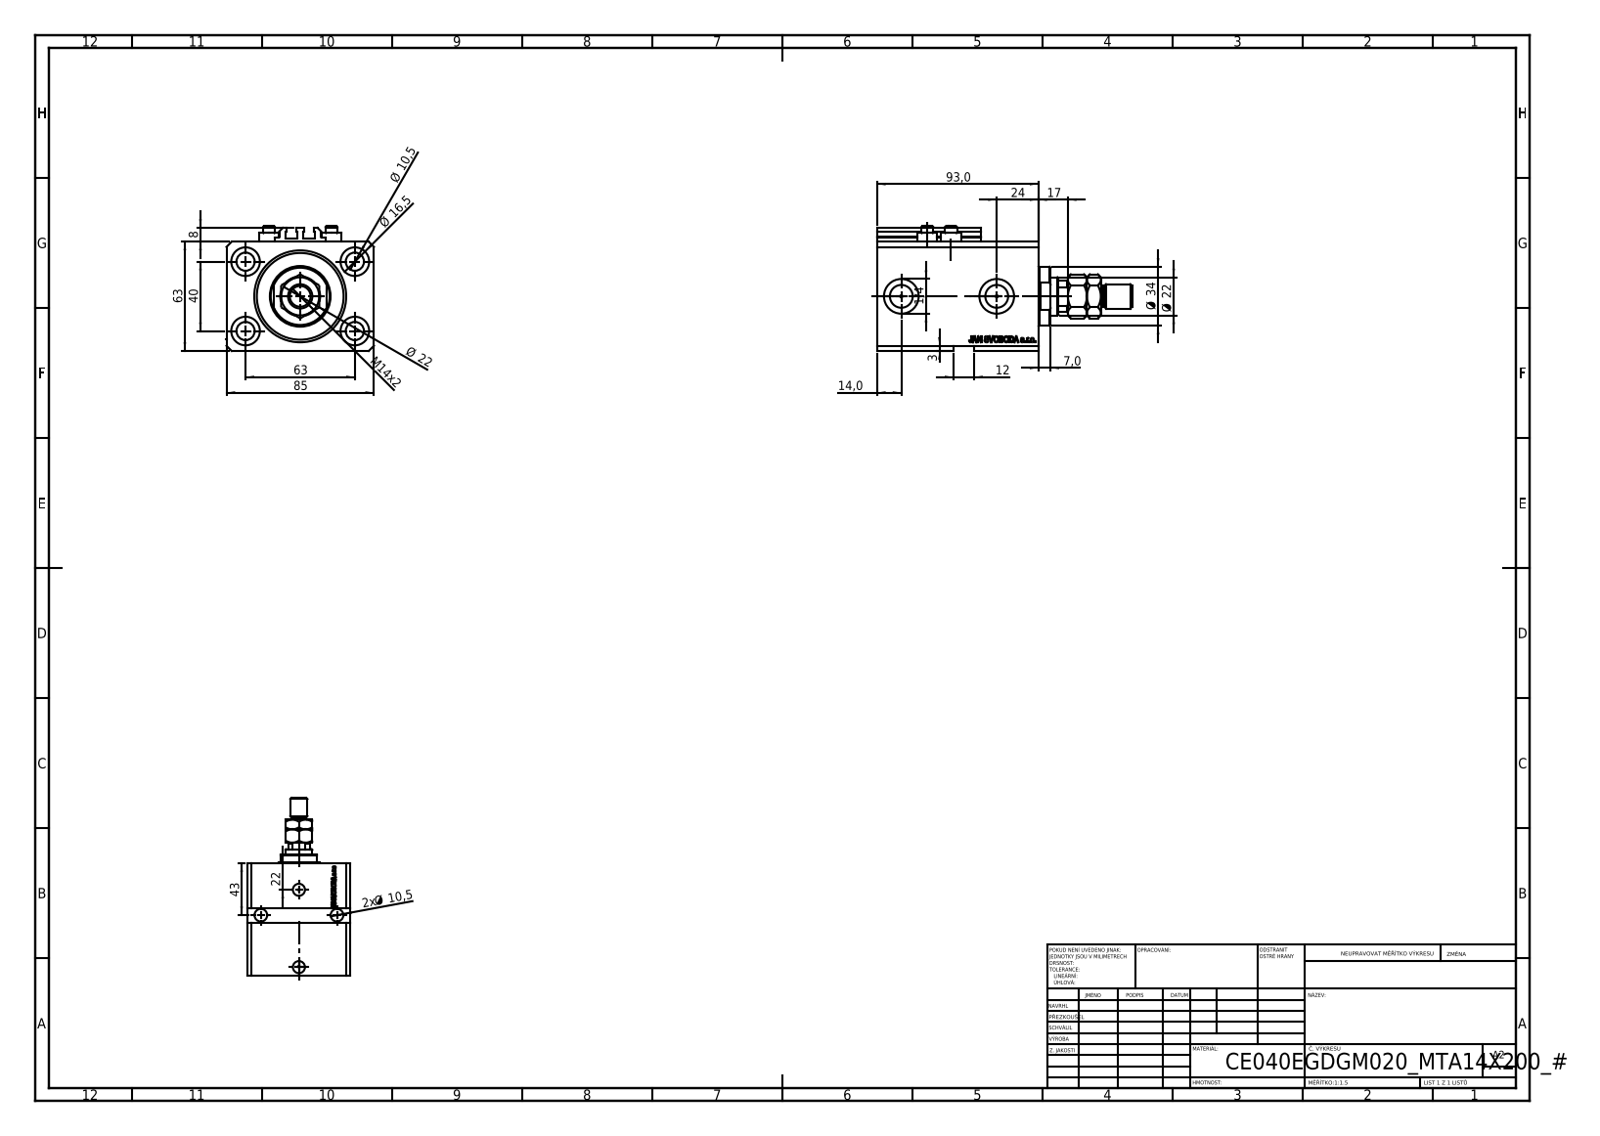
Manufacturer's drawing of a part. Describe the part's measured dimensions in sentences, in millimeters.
The part is named "ALLEN BOLT V250CE; V250CE_C_VCP; MTA; V250CE_VC_E (+1 more)". Its 3-D file was written by "SolidWorks 2019 (CONFIG_CONTROL_DESIGN)". It is 9 solids with 1152 faces: 554 planar, 142 cylindrical and 456 other. Overall it measures 147 by 85 by 72 millimeters. Its volume is 444 170 cubic millimeters and its surface area 99 985 square millimeters. Round holes: 6 of diameter 10.5, 4 of diameter 1.25, 4 of diameter 4, 4 of diameter 16.5, 2 of diameter 10, 2 of diameter 13.16, 2 of diameter 20, 1 of diameter 12.5, 1 of diameter 22, 1 of diameter 40, 1 of diameter 53. Round bosses or shafts: 4 of diameter 11.6, 4 of diameter 7, 1 of diameter 34, 1 of diameter 14, 1 of diameter 12. Partial cylindrical surfaces (rounded edges, fillets, slot ends): 10 of radius 0.2, 1 of radius 10.5. The main face-to-face distances are 63, 85, 17, 93, 76, 11.4, 64.6, 81.6, 65, 3. The hole center spacings are 37.31, 63, 13.6, 15.4, 24.96, 28.02, 28.43, 33.62.
